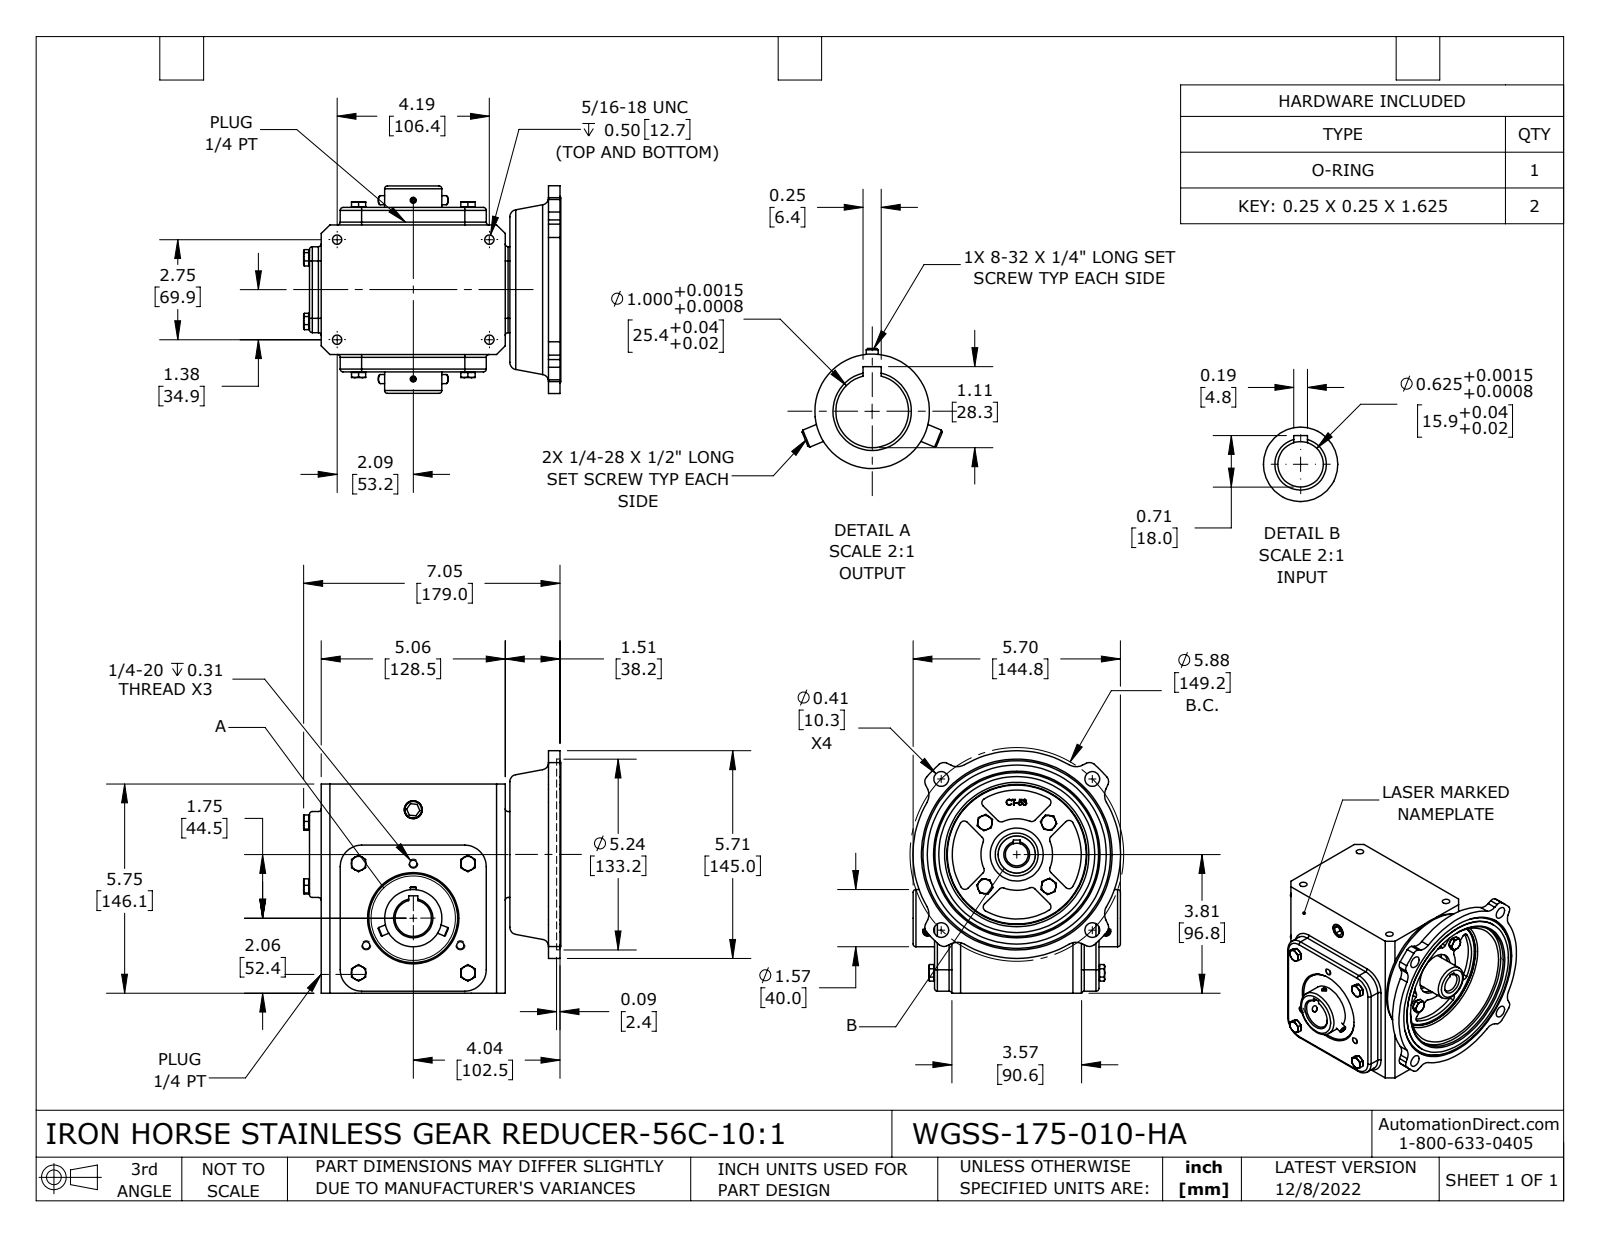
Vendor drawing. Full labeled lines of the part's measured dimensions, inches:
Part name (STEP PRODUCT): WGSS-175-010-HA
STEP written by: SolidWorks 2021 (CONFIG_CONTROL_DESIGN)
Units: inches
Bodies: 7 solids, 891 faces (390 planar, 231 cylindrical, 270 other)
Overall size (bounding box): 7.071 × 6.691 × 5.709
Volume: 127 in³ · Surface area: 281 in²
Round holes (diameter × count): ⌀0.213 ×4, ⌀0.257 ×4, ⌀0.406 ×4, ⌀0.201 ×3, ⌀0.136 ×2, ⌀0.625 ×1, ⌀0.866 ×1, ⌀1 ×1, ⌀1.102 ×1, ⌀1.457 ×1, ⌀1.575 ×1, ⌀3.819 ×1
Round bosses / shafts (diameter × count): ⌀0.394 ×8, ⌀0.25 ×4, ⌀0.164 ×2, ⌀4.921 ×1, ⌀2.441 ×1, ⌀1.575 ×1, ⌀1.181 ×1
Partial cylindrical surfaces — rounded edges, fillets, slot ends (radius × count): R0.079 ×28, R0.118 ×16, R0.394 ×12, R0.197 ×8, R0.591 ×4, R0.984 ×1, R1.772 ×1, R2.854 ×1
Main face-to-face distances: 0.48, 4.04, 5.75, 5.06, 0.157, 3.56, 4.52, 0.315, 6.565, 1.506
Hole centre spacings: 2.357, 2.937, 4.154, 1.496, 2.591, 4.913, 2.75, 4.188
